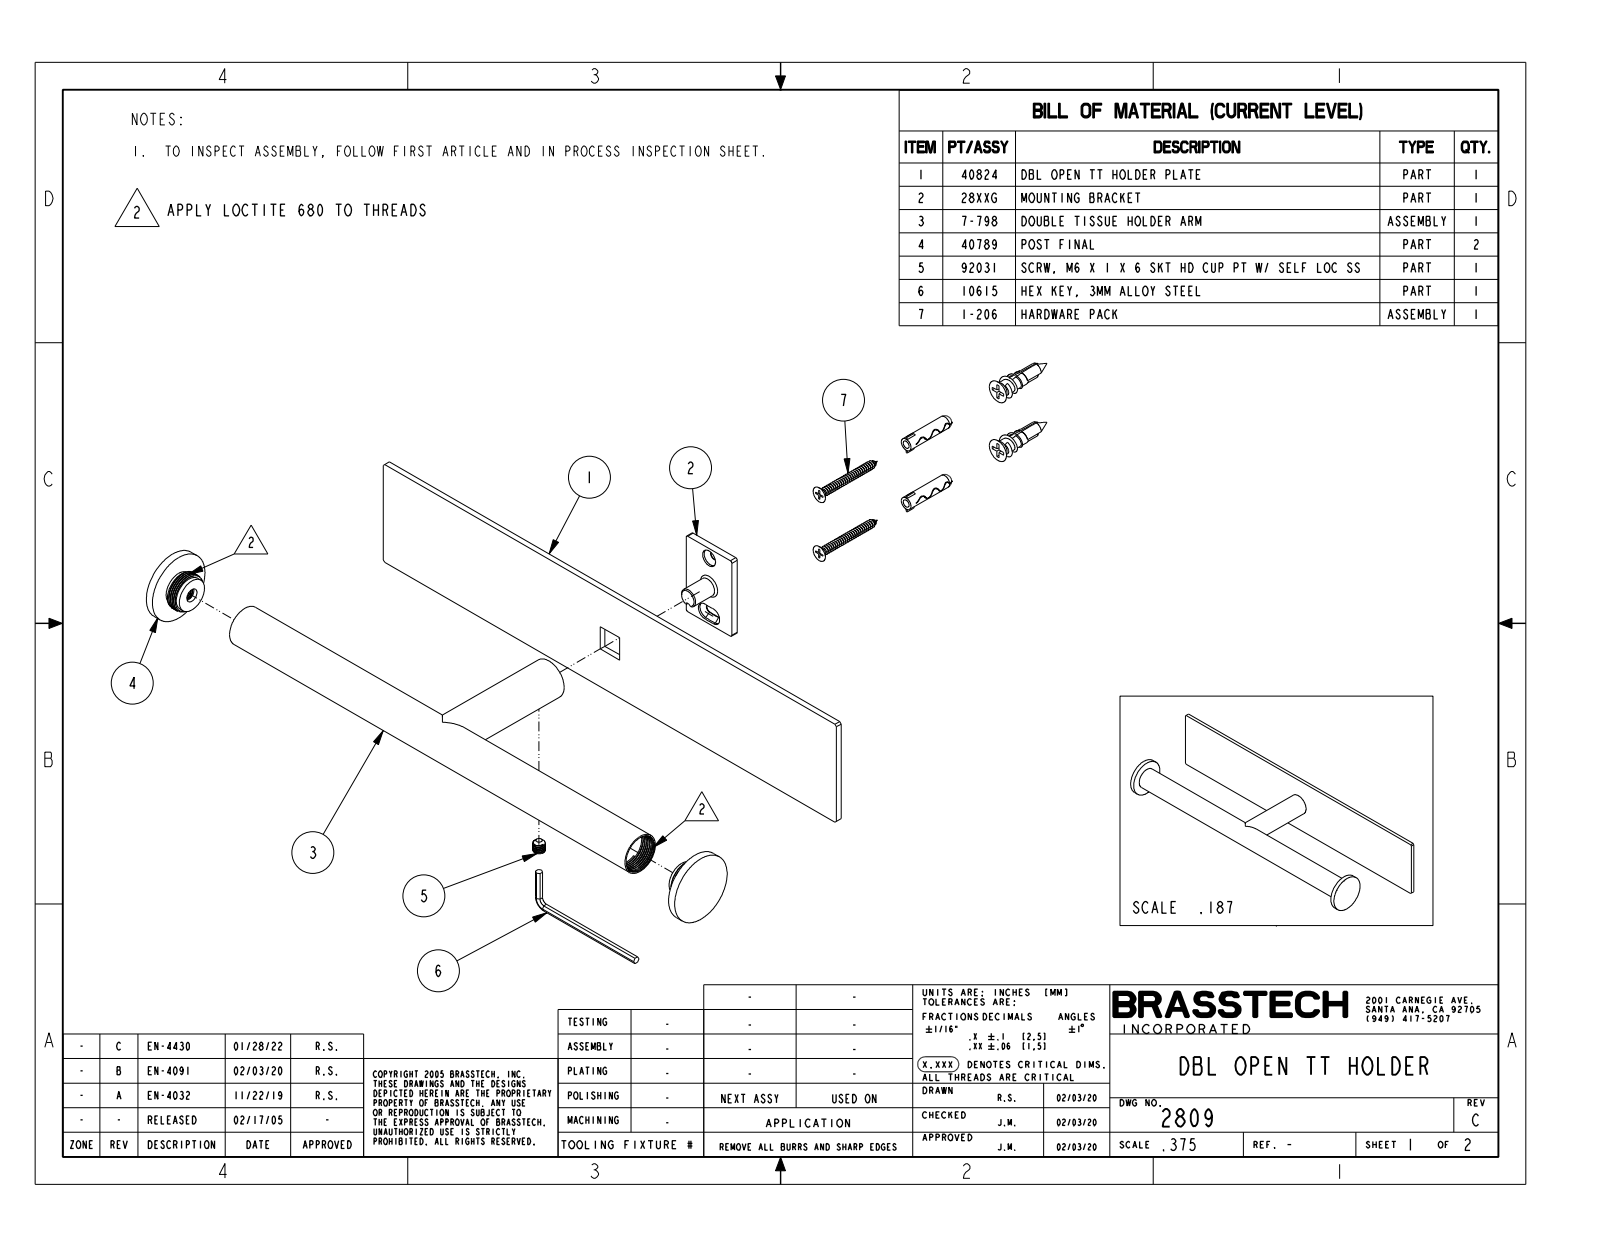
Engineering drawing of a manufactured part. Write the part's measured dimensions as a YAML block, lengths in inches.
part_name: "2809"
step_written_by: "CREO PARAMETRIC BY PTC INC, 2018400 (CONFIG_CONTROL_DESIGN)"
units: inches
bodies: {solids: 1, faces: 200, planar: 41, cylindrical: 101, other: 58}
overall_size: [11.732, 3.696, 2.2]
volume: 5.305
surface_area: 125.3
round_holes:
  - {diameter: 0.2, count: 2}
  - {diameter: 0.708, count: 2}
  - {diameter: 0.26, count: 1}
  - {diameter: 0.73, count: 1}
round_bosses_or_shafts:
  - {diameter: 0.787, count: 2}
  - {diameter: 0.5, count: 2}
  - {diameter: 0.453, count: 2}
  - {diameter: 1.358, count: 1}
  - {diameter: 0.65, count: 1}
  - {diameter: 0.442, count: 1}
partial_cylinders:
  - {radius: 0.04, count: 4}
  - {radius: 0.372, count: 1}
  - {radius: 0.388, count: 1}
face_to_face_distances: [0.12, 0.157, 10.394, 0.138, 0.258, 10.551, 2.2, 10.236, 9.894, 0.5]
